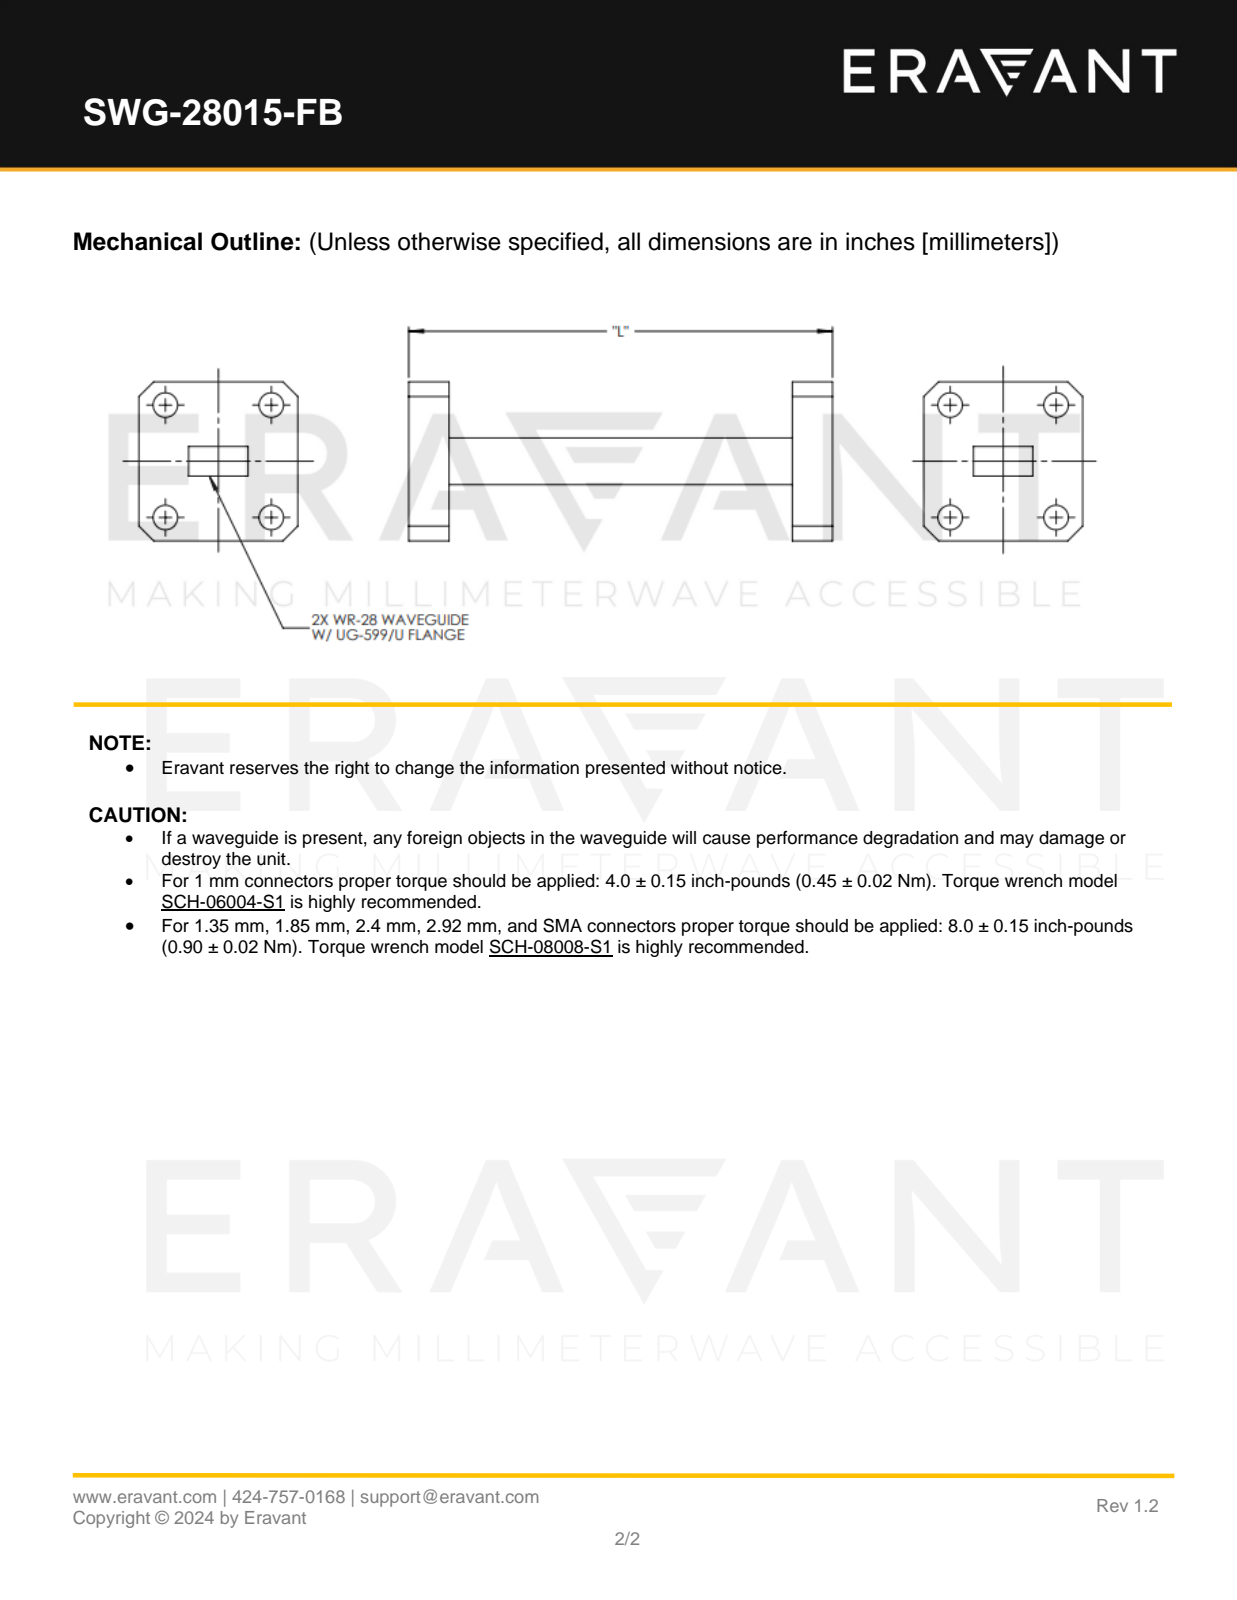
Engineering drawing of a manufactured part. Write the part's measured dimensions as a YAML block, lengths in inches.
part_name: "SWG-28015-FB"
step_written_by: "SolidWorks 2021 (CONFIG_CONTROL_DESIGN)"
units: inches
bodies: {solids: 1, faces: 50, planar: 34, cylindrical: 16, other: 0}
overall_size: [1.5, 0.75, 0.75]
volume: 0.282
surface_area: 4.831
round_holes:
  - {diameter: 0.116, count: 4}
face_to_face_distances: [0.19, 1.31, 1.5, 1.12, 0.22, 0.195, 0.555, 0.75, 0.36, 0.265]
hole_center_spacings: [0.5, 0.53, 0.729]
